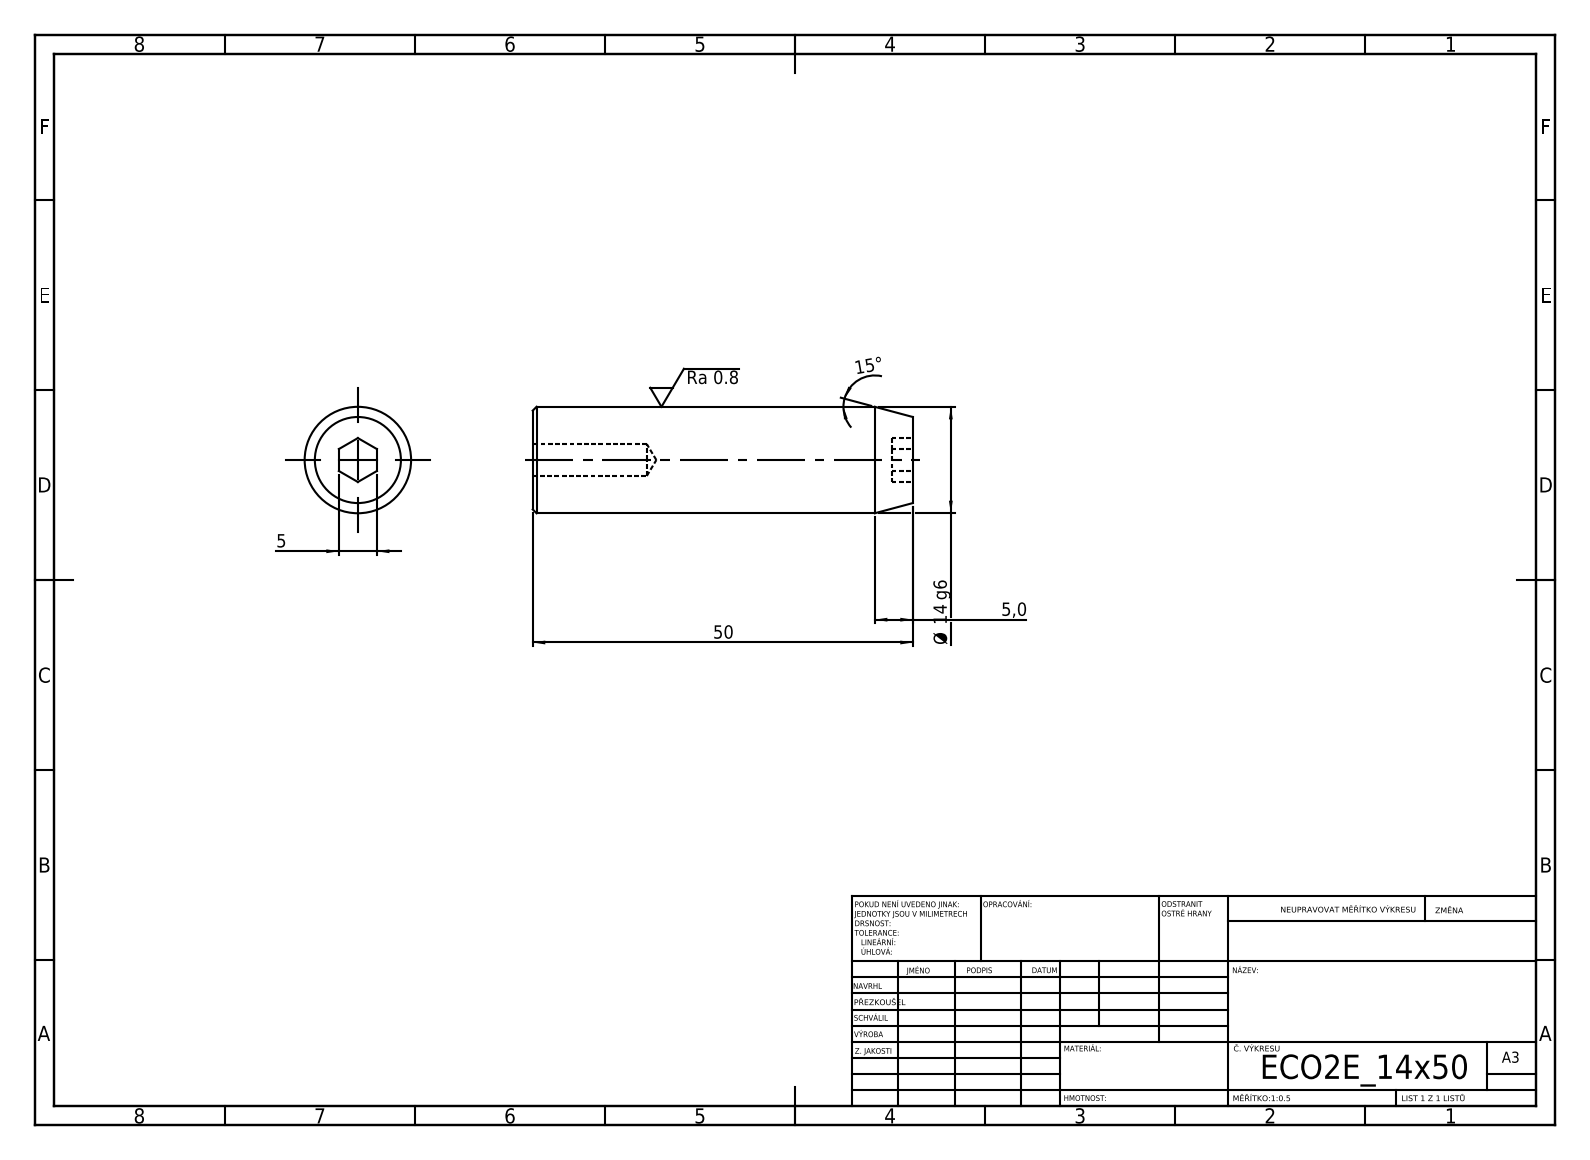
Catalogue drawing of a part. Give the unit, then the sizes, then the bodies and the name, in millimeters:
Units: millimetres
Overall size (bounding box): 50 × 14 × 14
Round holes (diameter × count): ⌀4.2 ×1
Round bosses / shafts (diameter × count): ⌀14 ×1
Main face-to-face distances: 50, 5, 2.8, 47.2
Volume: 7 279 mm³ · Surface area: 2 675 mm²
Bodies: 1 solid, 19 faces (9 planar, 4 cylindrical, 6 other)
STEP written by: SolidWorks 2019 (CONFIG_CONTROL_DESIGN)
